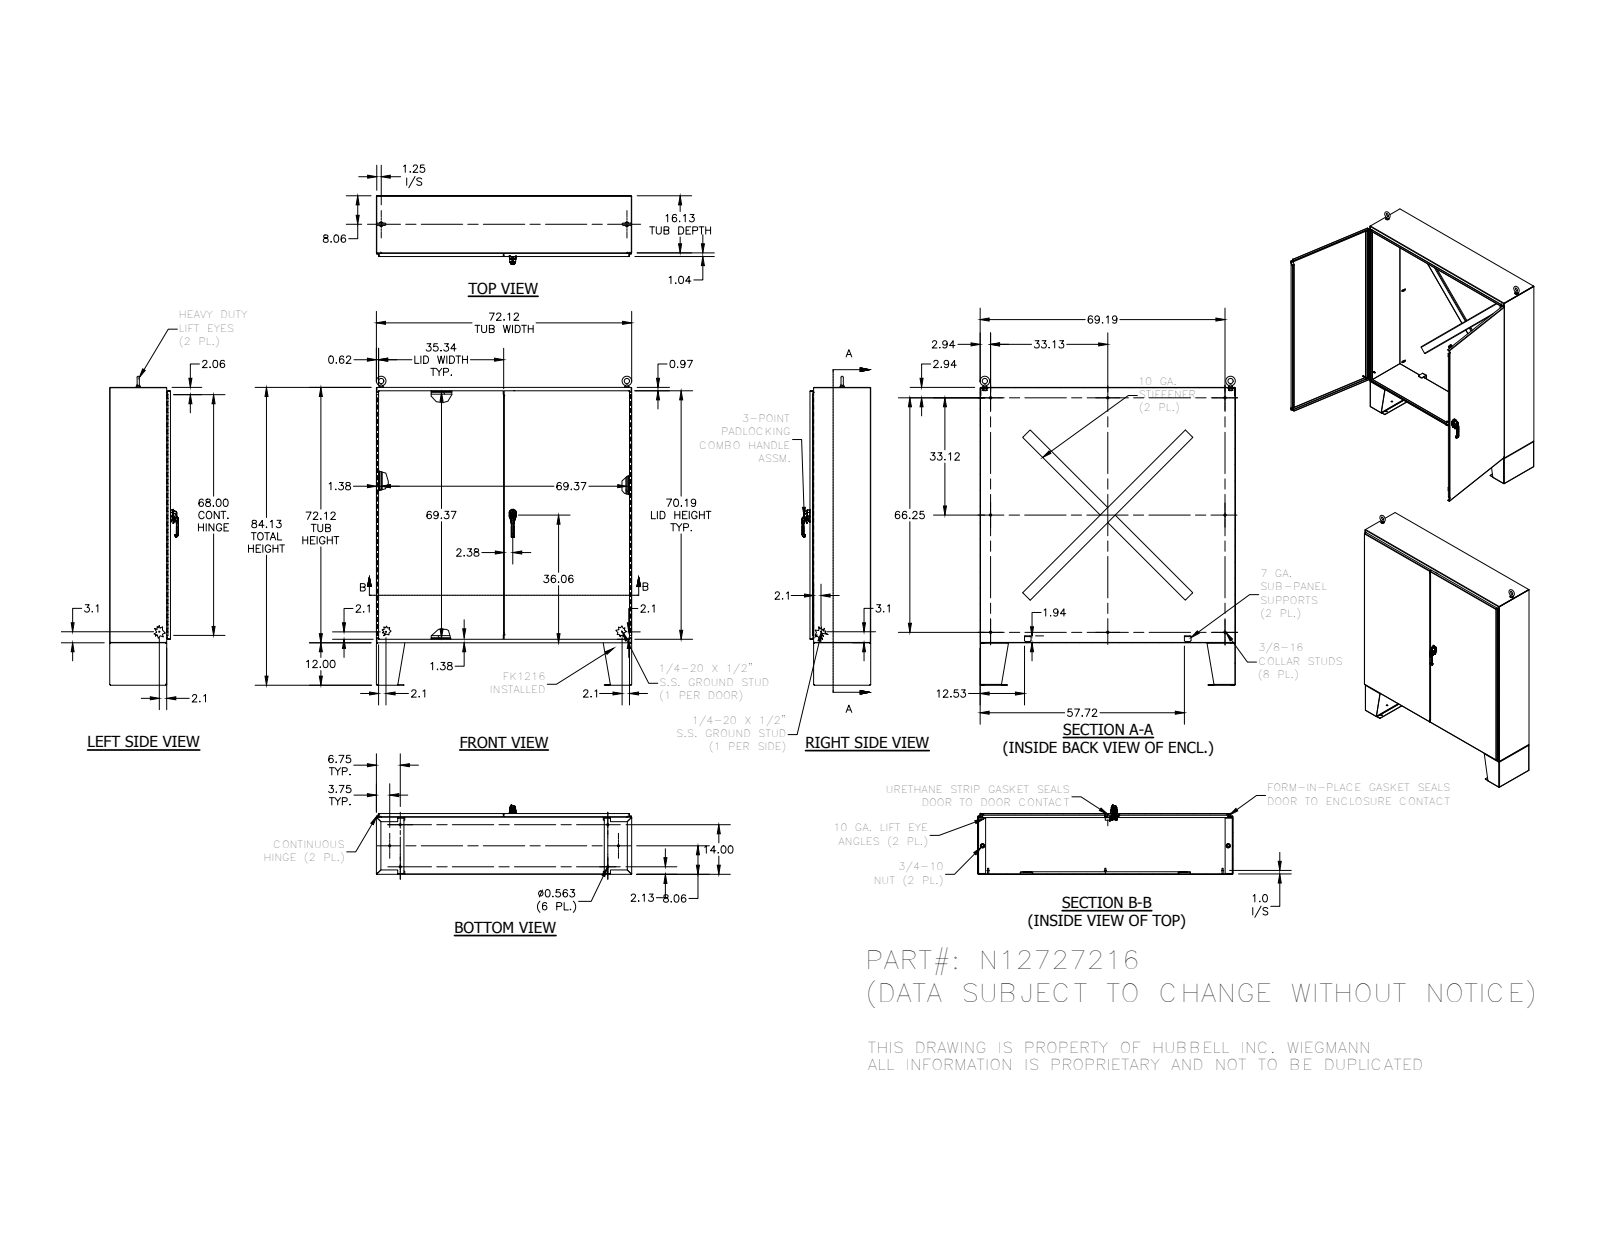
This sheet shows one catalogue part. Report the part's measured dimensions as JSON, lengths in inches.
{"part_name": "N12727216", "step_written_by": "SolidWorks 2018 (AUTOMOTIVE_DESIGN)", "units": "inches", "bodies": {"solids": 76, "faces": 2596, "planar": 1528, "cylindrical": 768, "other": 300}, "overall_size": [87.248, 72.946, 19.338], "volume_in3": 1821, "surface_area_in2": 36959, "round_holes": [[0.563, 18], [0.277, 8], [0.2, 4], [0.28, 3], [0.125, 2], [0.125, 2], [0.241, 2], [0.25, 2], [0.252, 2], [0.4, 2], [0.45, 2], [0.642, 2]], "round_bosses_or_shafts": [[0.33, 8], [0.625, 7], [0.25, 5], [0.337, 3], [1.25, 2], [1.12, 2], [1, 2], [0.75, 2]], "partial_cylinders_radius": [[0.031, 24], [0.094, 23], [0.219, 22], [0.05, 18], [0.025, 16], [0.125, 15], [0.03, 13], [0.067, 8]], "face_to_face_distances": [0.094, 17.067, 16.973, 17.16, 72.031, 72.125, 71.938, 0.125, 16.031, 1.035], "hole_center_spacings": [5, 5.85, 6.57, 6.652, 8.03, 14.75, 15.574, 58.393]}
